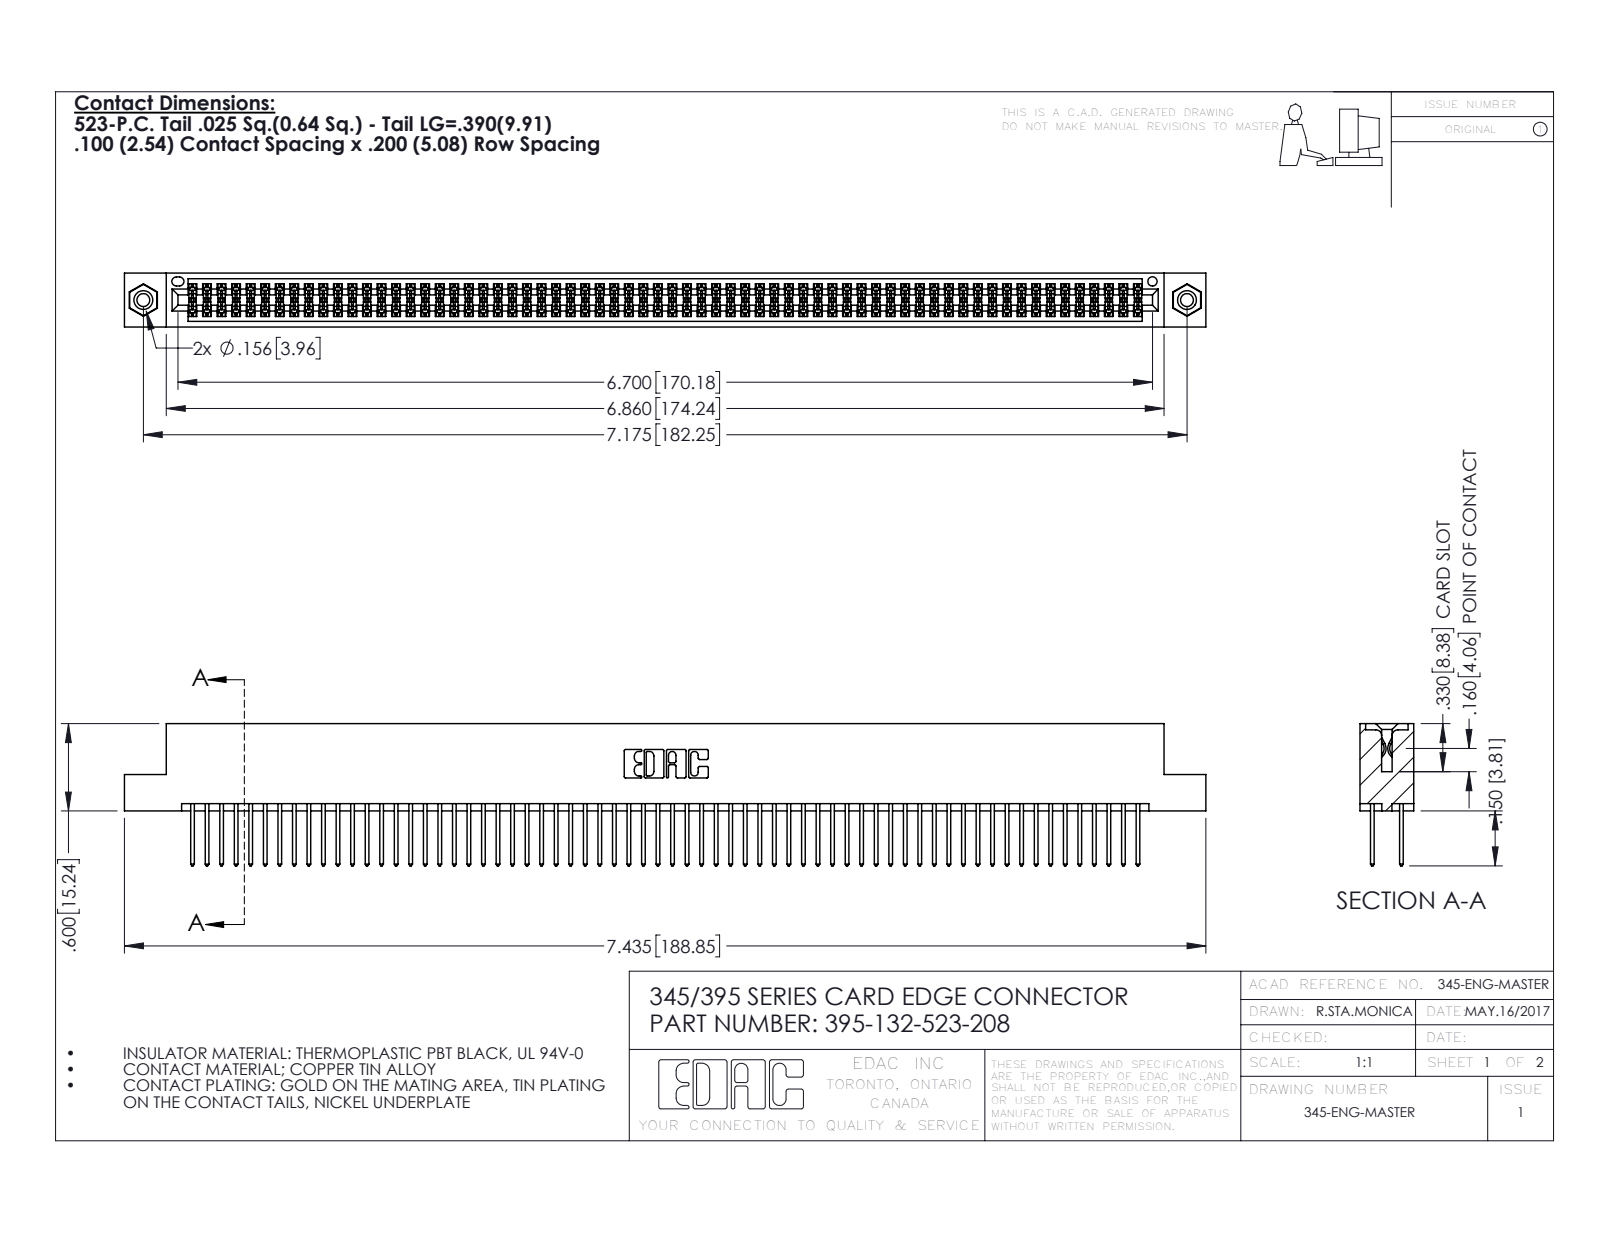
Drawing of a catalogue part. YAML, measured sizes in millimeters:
part_name: "345 Part_Flush Mounting Lugs - 0.156 Dia-TI; 395-132-523-208; 345-250-001_345-250-003-102; 345-292-001_345-293-123"
step_written_by: "SolidWorks 2016 (CONFIG_CONTROL_DESIGN)"
units: millimeters
bodies: {solids: 135, faces: 6786, planar: 4468, cylindrical: 2302, other: 16}
overall_size: [188.8, 24.8, 9.4]
volume: 18830
surface_area: 29530
round_holes:
  - {diameter: 2.3, count: 2}
  - {diameter: 3.2, count: 2}
  - {diameter: 4, count: 2}
  - {diameter: 1.6, count: 1}
round_bosses_or_shafts:
  - {diameter: 3.9, count: 2}
partial_cylinders:
  - {radius: 0.2, count: 198}
  - {radius: 0.3, count: 132}
  - {radius: 0.3, count: 22}
  - {radius: 0.2, count: 6}
  - {radius: 0.8, count: 6}
  - {radius: 0.7, count: 3}
  - {radius: 0.4, count: 2}
  - {radius: 0.5, count: 2}
face_to_face_distances: [1.8, 7.6, 5.1, 2.5, 6.9, 0.6, 9.4, 5.7, 4.4, 3.8]
hole_center_spacings: [6.9, 176.3, 182.2]
